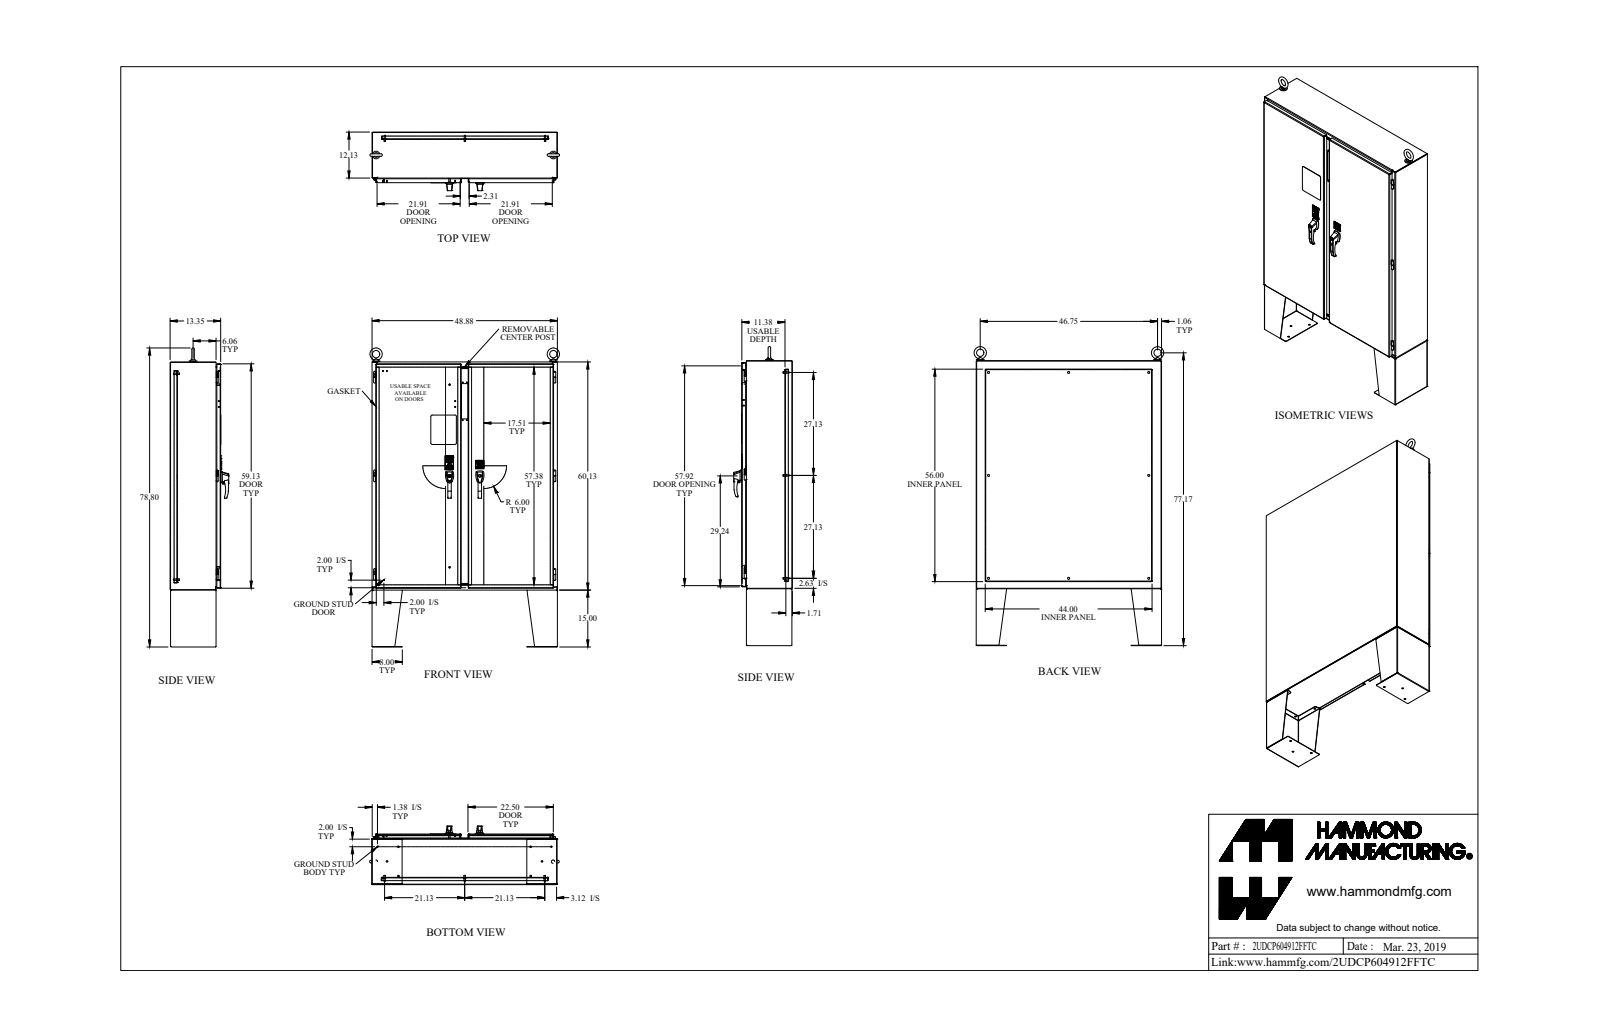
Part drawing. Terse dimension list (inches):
name: 2UDCP604912FFTC
written by: SolidWorks 2018 (AUTOMOTIVE_DESIGN)
unit: in
bodies: 178 solids, 2694 faces (1564 planar, 810 cylindrical, 320 other)
size: 78.799 × 49.997 × 15.465
volume: 2 786 in³; area: 30 120 in²
holes: 14× ⌀0.437, 10× ⌀0.307, 9× ⌀0.281, 8× ⌀0.25, 8× ⌀0.35, 6× ⌀0.313, 5× ⌀0.196, 5× ⌀0.445, 4× ⌀0.257, 4× ⌀0.28, 4× ⌀0.39, 4× ⌀0.413
bosses: 14× ⌀0.25, 12× ⌀1, 9× ⌀0.375, 8× ⌀0.65, 8× ⌀0.33, 8× ⌀0.281, 5× ⌀0.625, 4× ⌀0.75
rounds: 54× R0.06, 44× R0.125, 38× R0.5, 32× R0.017, 29× R0.185, 16× R0.048, 16× R0.143, 12× R0.03
face distances: 0.125, 0.072, 11.431, 13.368, 13.243, 1.937, 1.812, 1.865, 1.741, 11.503
hole spacings: 7.996, 4.888, 6.228, 8.074, 9.964, 10.99, 38.072, 41.015
